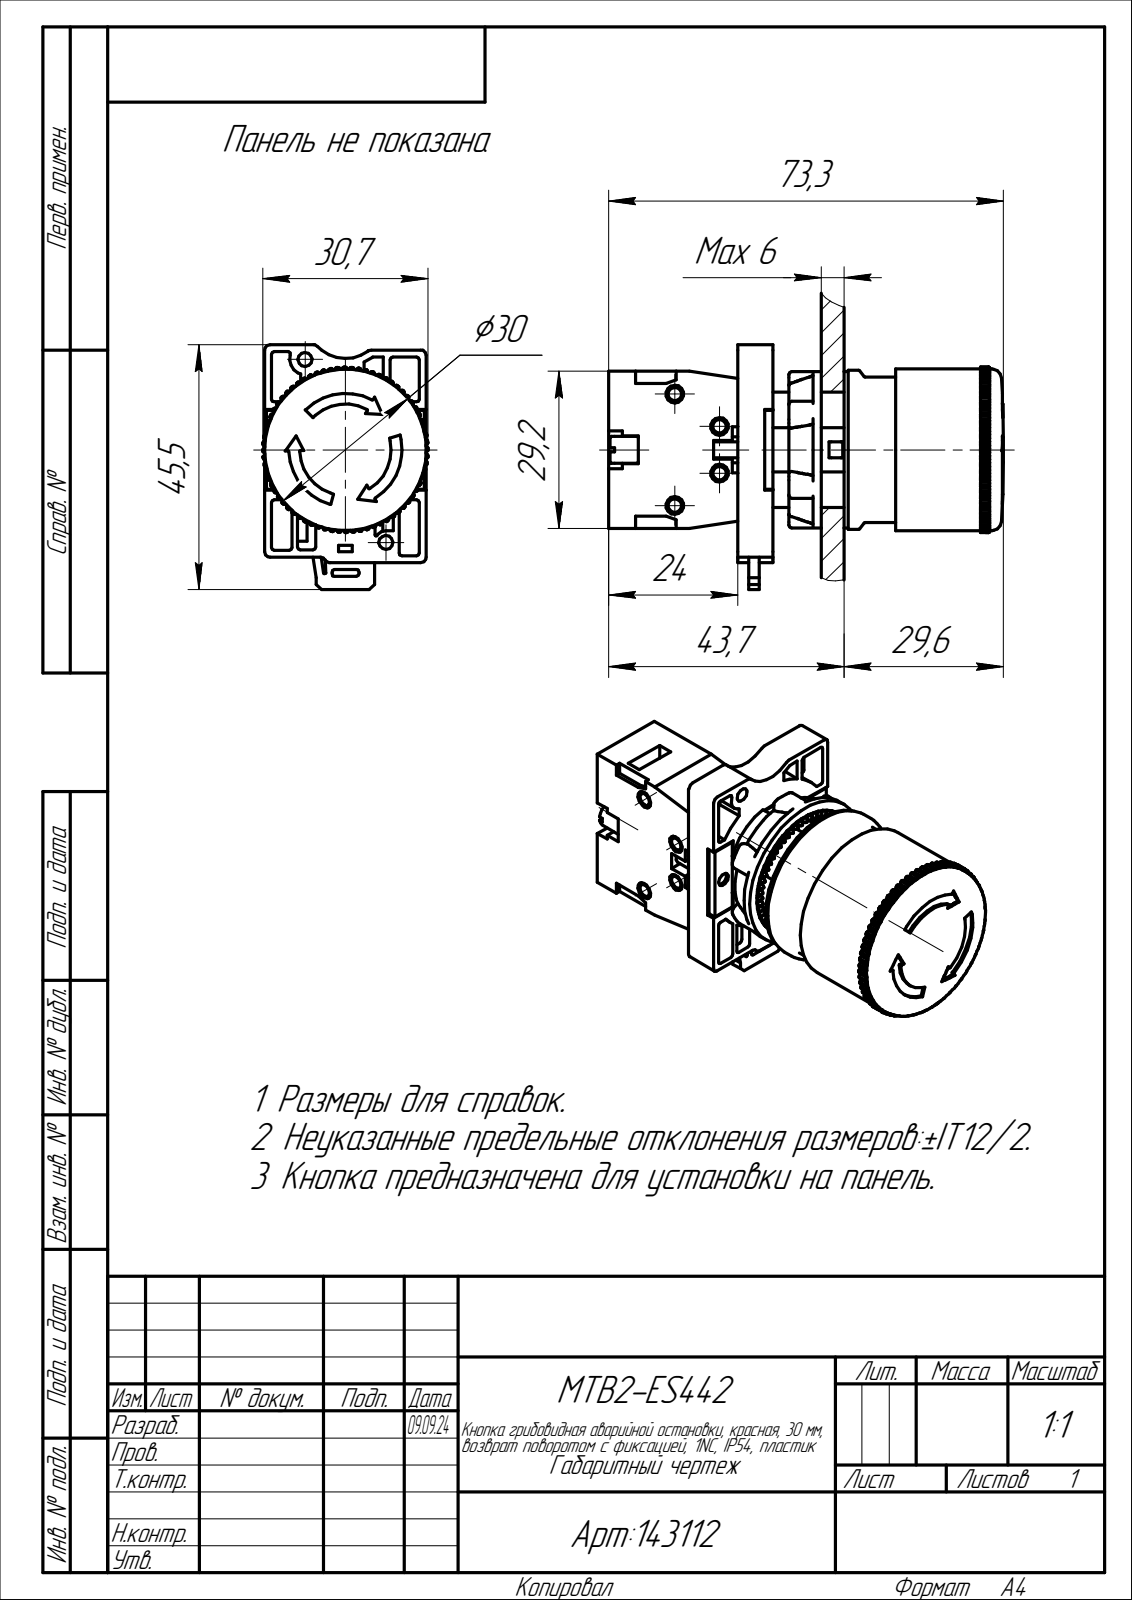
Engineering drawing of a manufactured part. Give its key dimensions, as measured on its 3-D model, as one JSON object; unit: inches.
{"step_written_by": "PRO/ENGINEER BY PARAMETRIC TECHNOLOGY CORPORATION, 2010280 (CONFIG_CONTROL_DESIGN)", "units": "inches", "bodies": {"solids": 1, "faces": 1368, "planar": 556, "cylindrical": 503, "other": 309}, "overall_size": [2.886, 1.791, 1.209], "volume_in3": 2.428, "surface_area_in2": 22.11, "round_holes": [[0.13, 4], [0.098, 2], [0.102, 2], [0.094, 1], [0.827, 1]], "round_bosses_or_shafts": [[0.098, 4], [0.244, 2], [0.138, 2], [1.181, 1], [1.161, 1], [1.142, 1], [1.063, 1], [0.197, 1]], "partial_cylinders_radius": [[0.008, 156], [0.02, 20], [0.039, 20], [0.012, 8], [0.004, 6], [0.031, 2], [0.089, 2], [0.126, 2]], "face_to_face_distances": [0.256, 0.587, 0.197, 0.589, 0.776, 0.945, 0.52, 1.555, 0.165, 1.201], "hole_center_spacings": [0.403, 0.486, 0.665, 0.343, 0.689, 0.704, 0.724, 0.739]}
